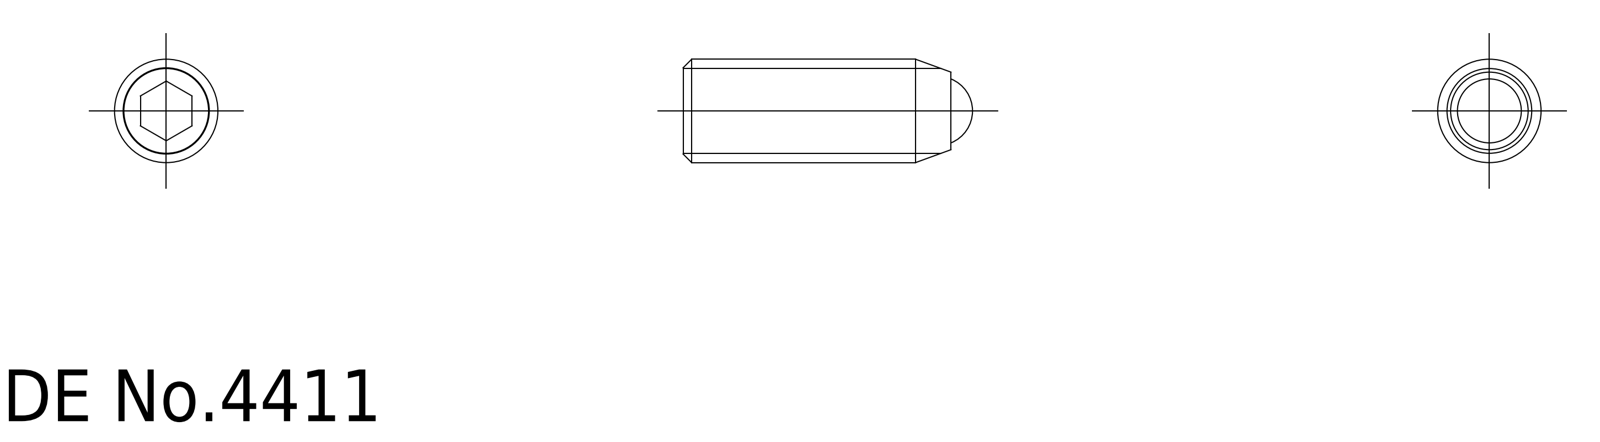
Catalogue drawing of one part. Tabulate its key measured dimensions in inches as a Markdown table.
| quantity | value |
| --- | --- |
| part name | ball; SCSS_M6_16_R_19070_36 |
| STEP written by | CADfix (AUTOMOTIVE_DESIGN) |
| units | inches |
| bodies | 2 solids, 20 faces (0 planar, 0 cylindrical, 20 other) |
| overall size | 0.661 × 0.236 × 0.236 |
| volume | 0.023 in³ |
| surface area | 0.738 in² |
